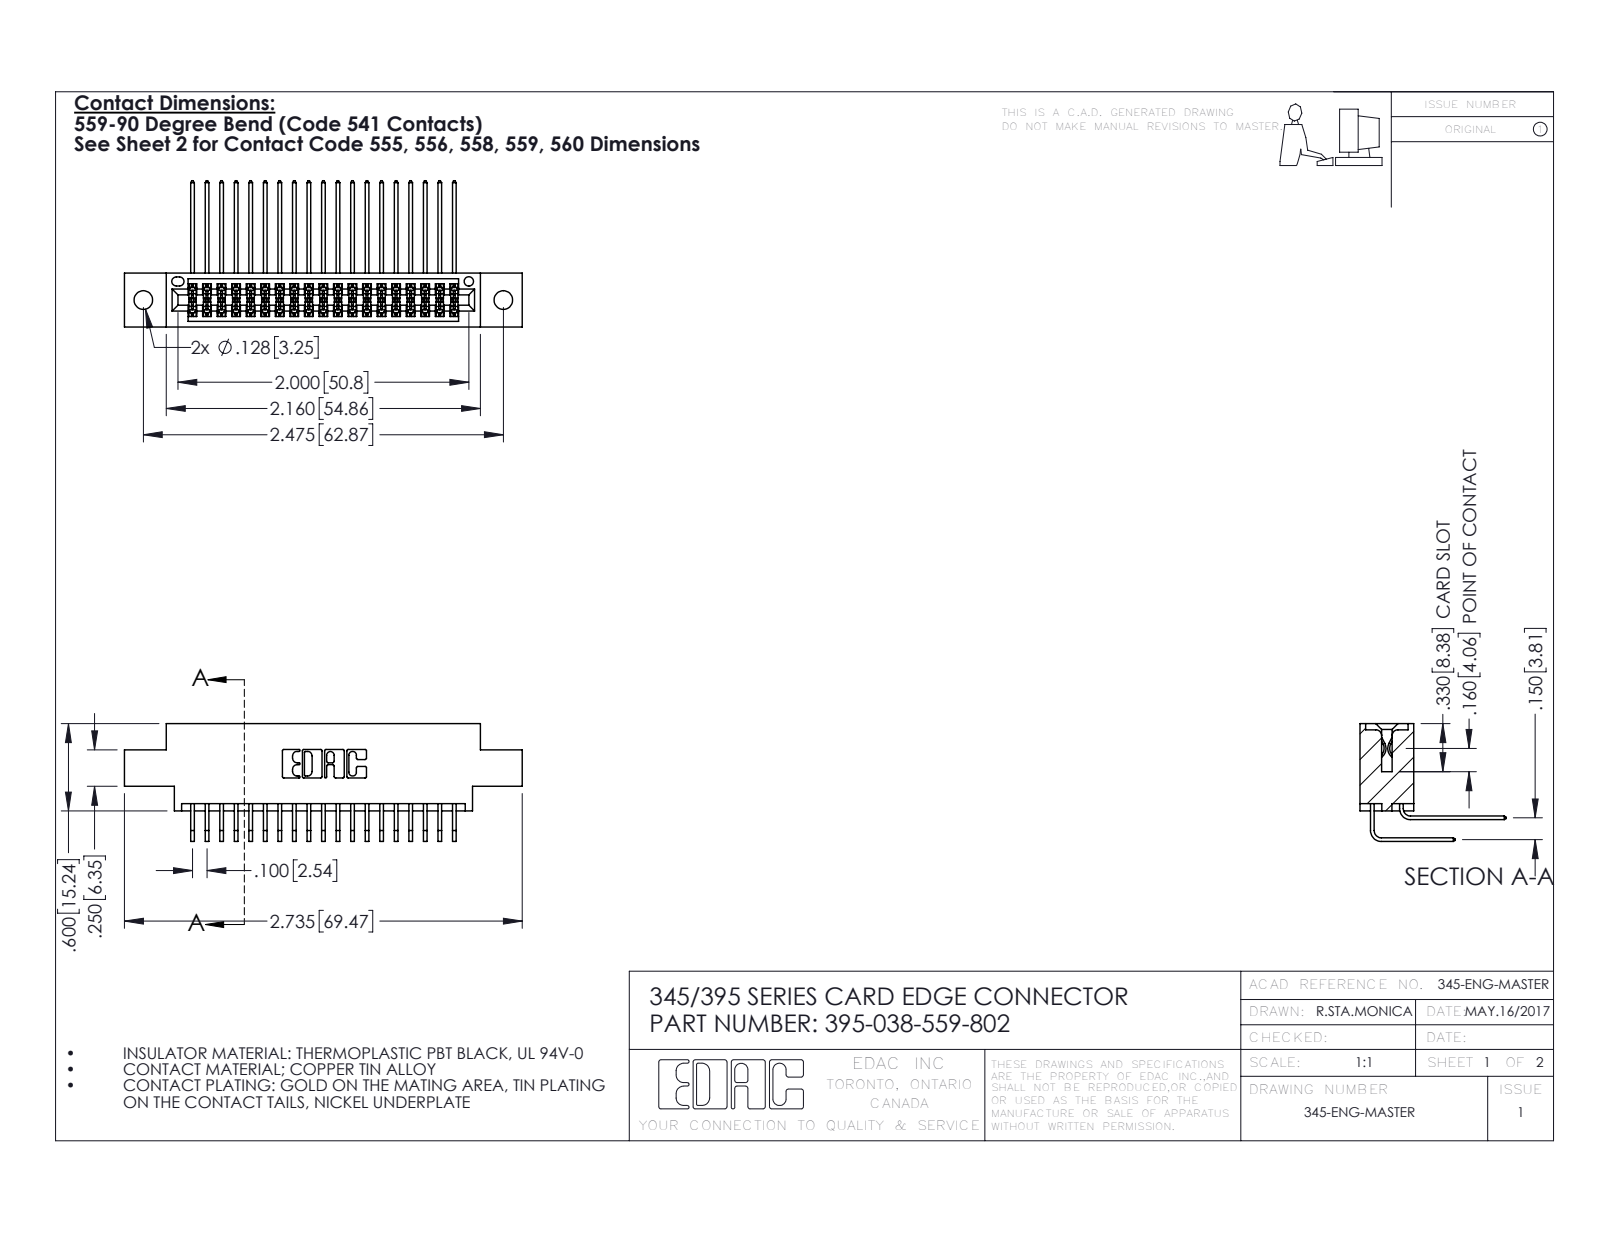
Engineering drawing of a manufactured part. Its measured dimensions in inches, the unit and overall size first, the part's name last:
Units: inches
Overall size (bounding box): 2.735 × 1.005 × 0.809
Round holes (diameter × count): ⌀0.128 ×2, ⌀0.064 ×1
Partial cylindrical surfaces — rounded edges, fillets, slot ends (radius × count): R0.006 ×58, R0.01 ×22, R0.007 ×6, R0.031 ×6, R0.026 ×3, R0.014 ×2, R0.019 ×2, R0.022 ×2
Main face-to-face distances: 0.072, 0.298, 0.37, 0.2, 0.098, 0.272, 0.025, 0.15, 0.225, 0.175
Hole centre spacings: 0.27, 2.241, 2.475
Volume: 0.403 in³ · Surface area: 15.84 in²
Bodies: 39 solids, 2106 faces (1414 planar, 692 cylindrical, 0 other)
Part name (STEP PRODUCT): 395-038-559-802; 345 Part_0.170 Offset - 0.128 Dia; 345-292-001_559 Tail - 2; 345-292-001_558 559 Tail - 1
STEP written by: SolidWorks 2016 (CONFIG_CONTROL_DESIGN)
